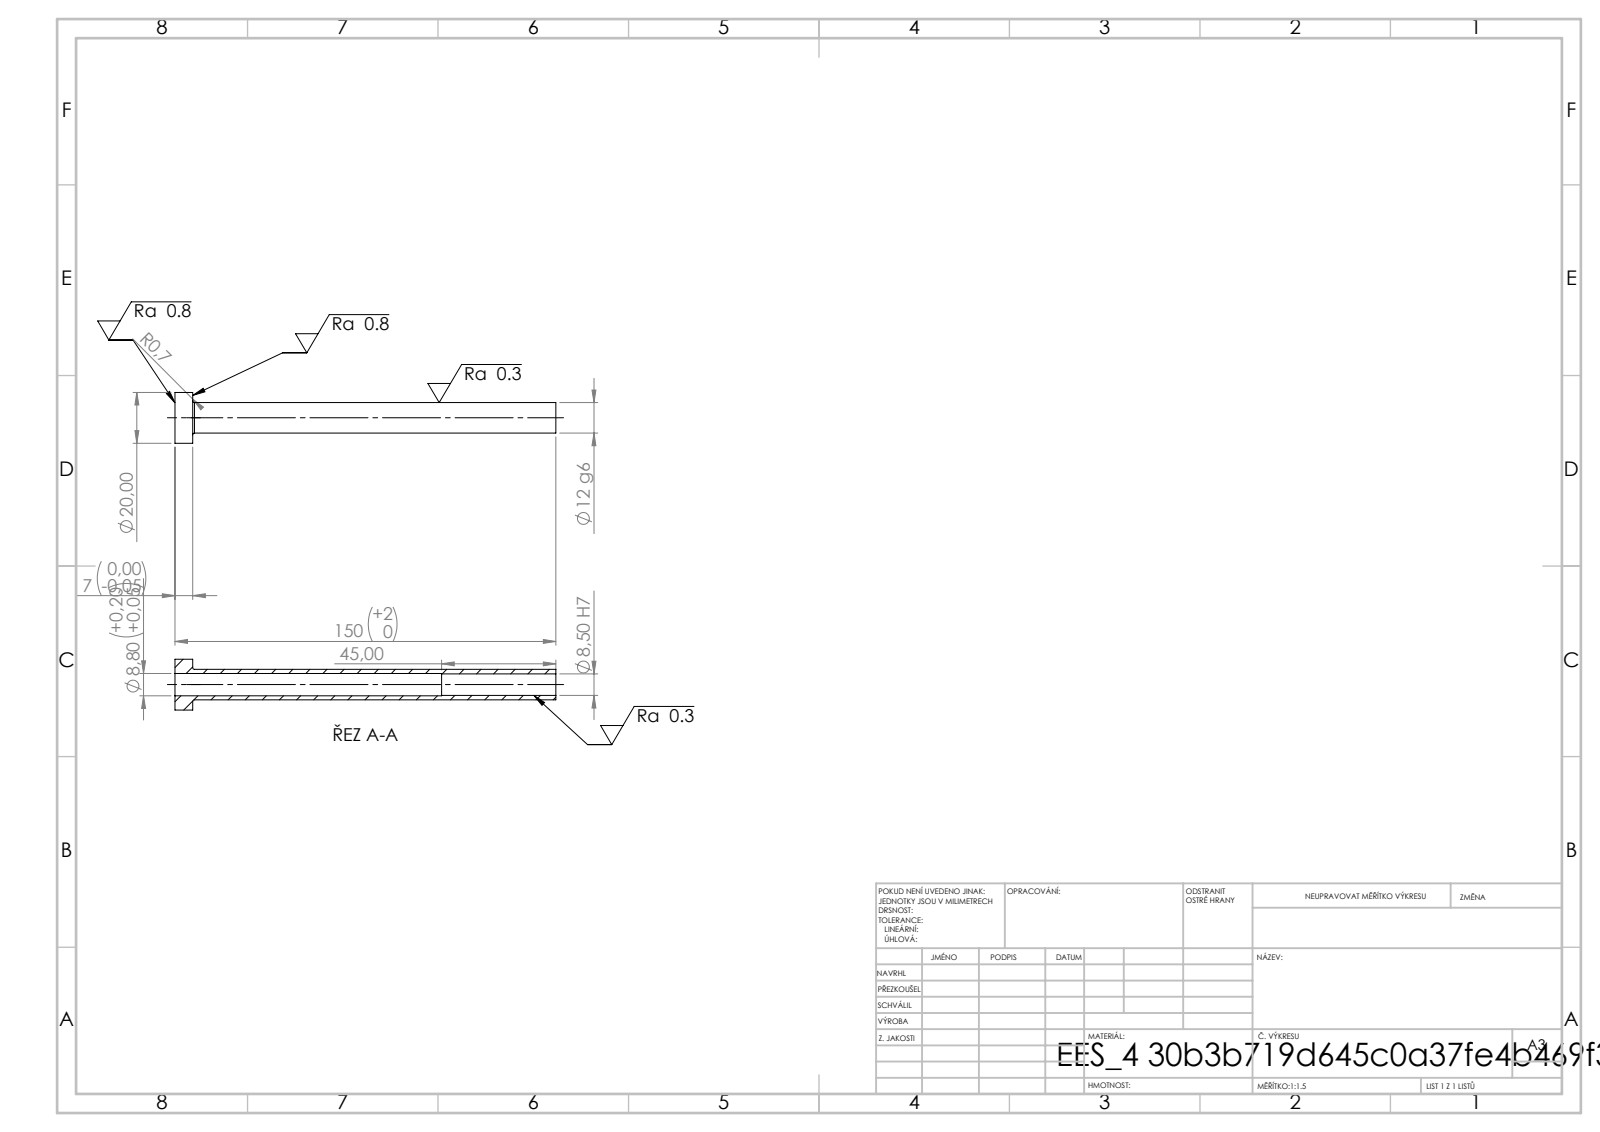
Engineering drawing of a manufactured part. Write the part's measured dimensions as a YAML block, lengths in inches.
step_written_by: "SolidWorks 2019 (CONFIG_CONTROL_DESIGN)"
units: inches
bodies: {solids: 1, faces: 14, planar: 4, cylindrical: 8, other: 2}
overall_size: [5.906, 0.787, 0.787]
volume: 0.576
surface_area: 16.18
round_holes:
  - {diameter: 0.335, count: 1}
  - {diameter: 0.346, count: 1}
round_bosses_or_shafts:
  - {diameter: 0.787, count: 1}
  - {diameter: 0.472, count: 1}
face_to_face_distances: [0.276, 5.906, 5.63, 4.134, 3.858, 1.772]
